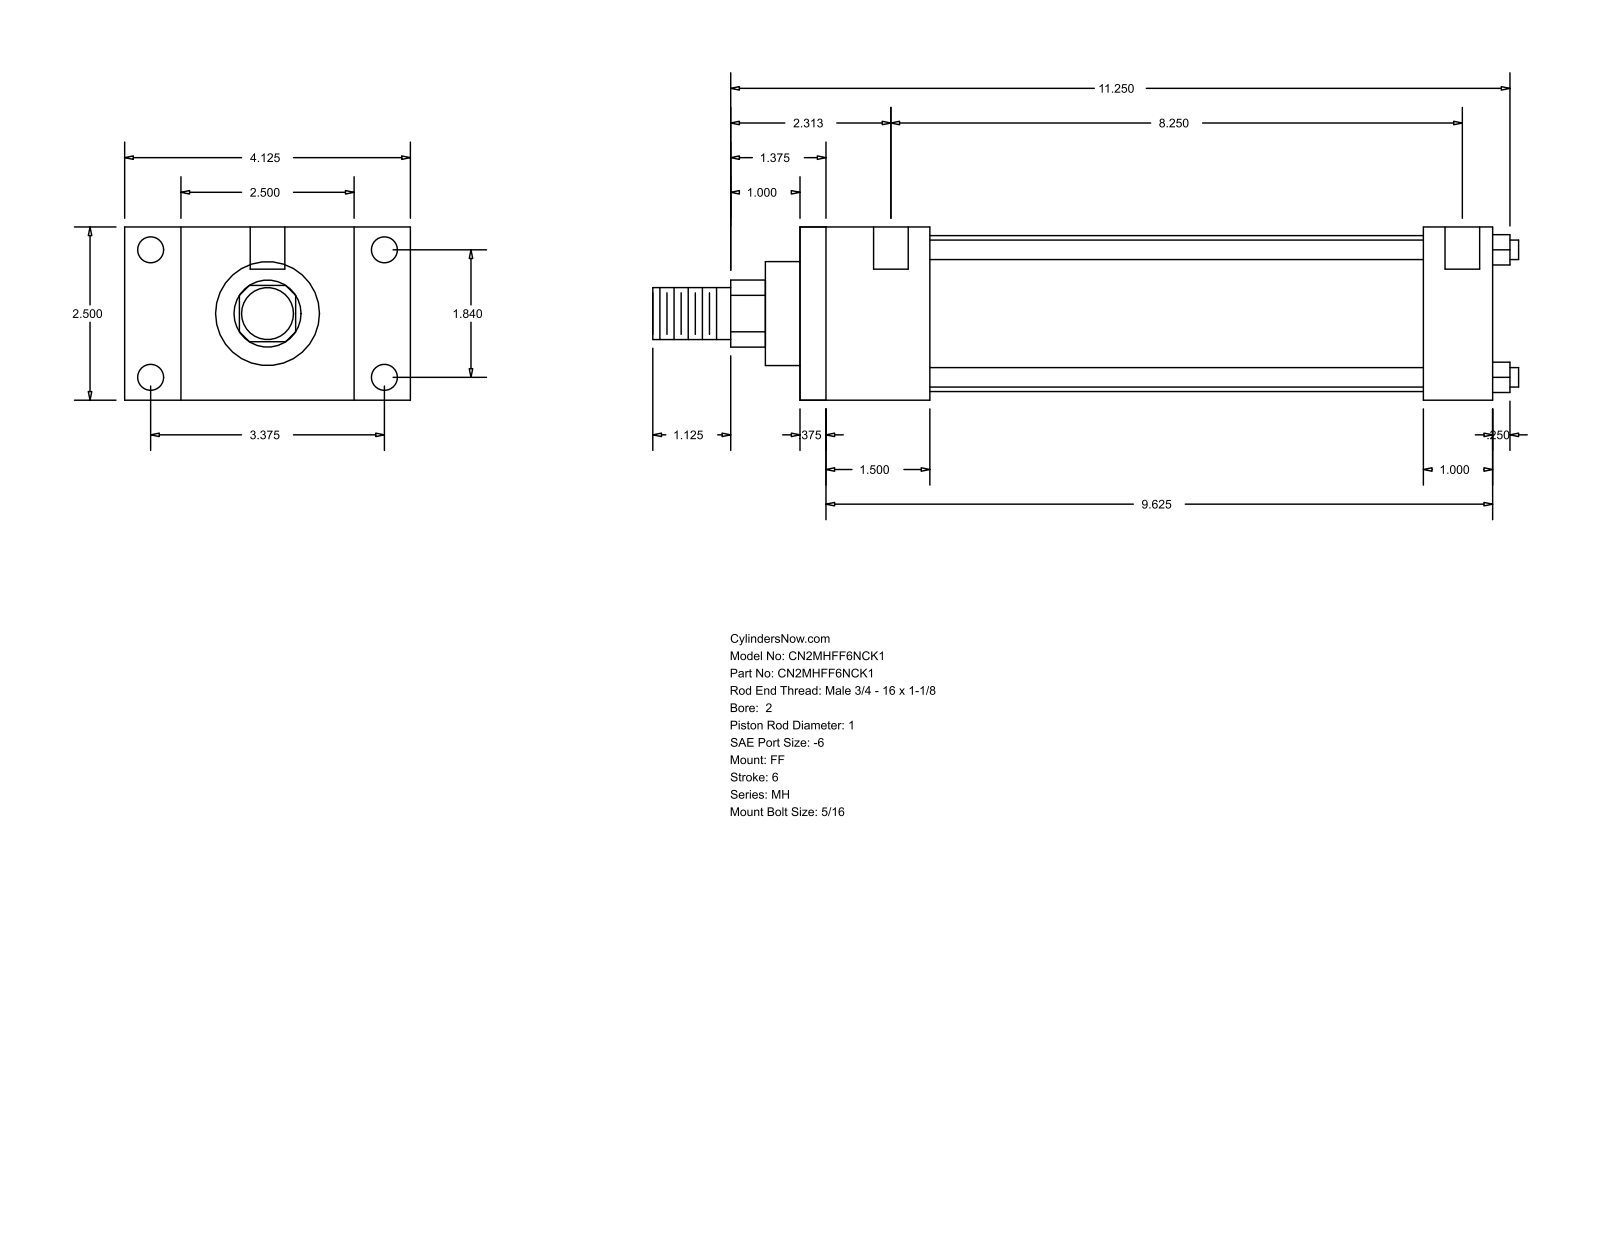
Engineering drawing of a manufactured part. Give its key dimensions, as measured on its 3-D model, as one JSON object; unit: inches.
{"part_name": "MH_FF__0200_1", "step_written_by": "GSSL Pune (CONFIG_CONTROL_DESIGN)", "units": "inches", "bodies": {"solids": 0, "faces": 92, "planar": 64, "cylindrical": 28, "other": 0}, "overall_size": [12.5, 4.125, 2.5], "round_holes": [[0.219, 4], [0.375, 4], [0.5, 2]], "round_bosses_or_shafts": [[0.281, 4], [2.25, 1], [1.5, 1], [1, 1], [0.75, 1]], "partial_cylinders_radius": [[0.484, 1]], "face_to_face_distances": [2.5, 10, 0.375, 9.625, 0.813, 1, 1.875, 9, 1.5, 8.625], "hole_center_spacings": [1.84, 3.375, 3.844, 8.562, 0.125, 0.187, 8.25, 8.375]}
